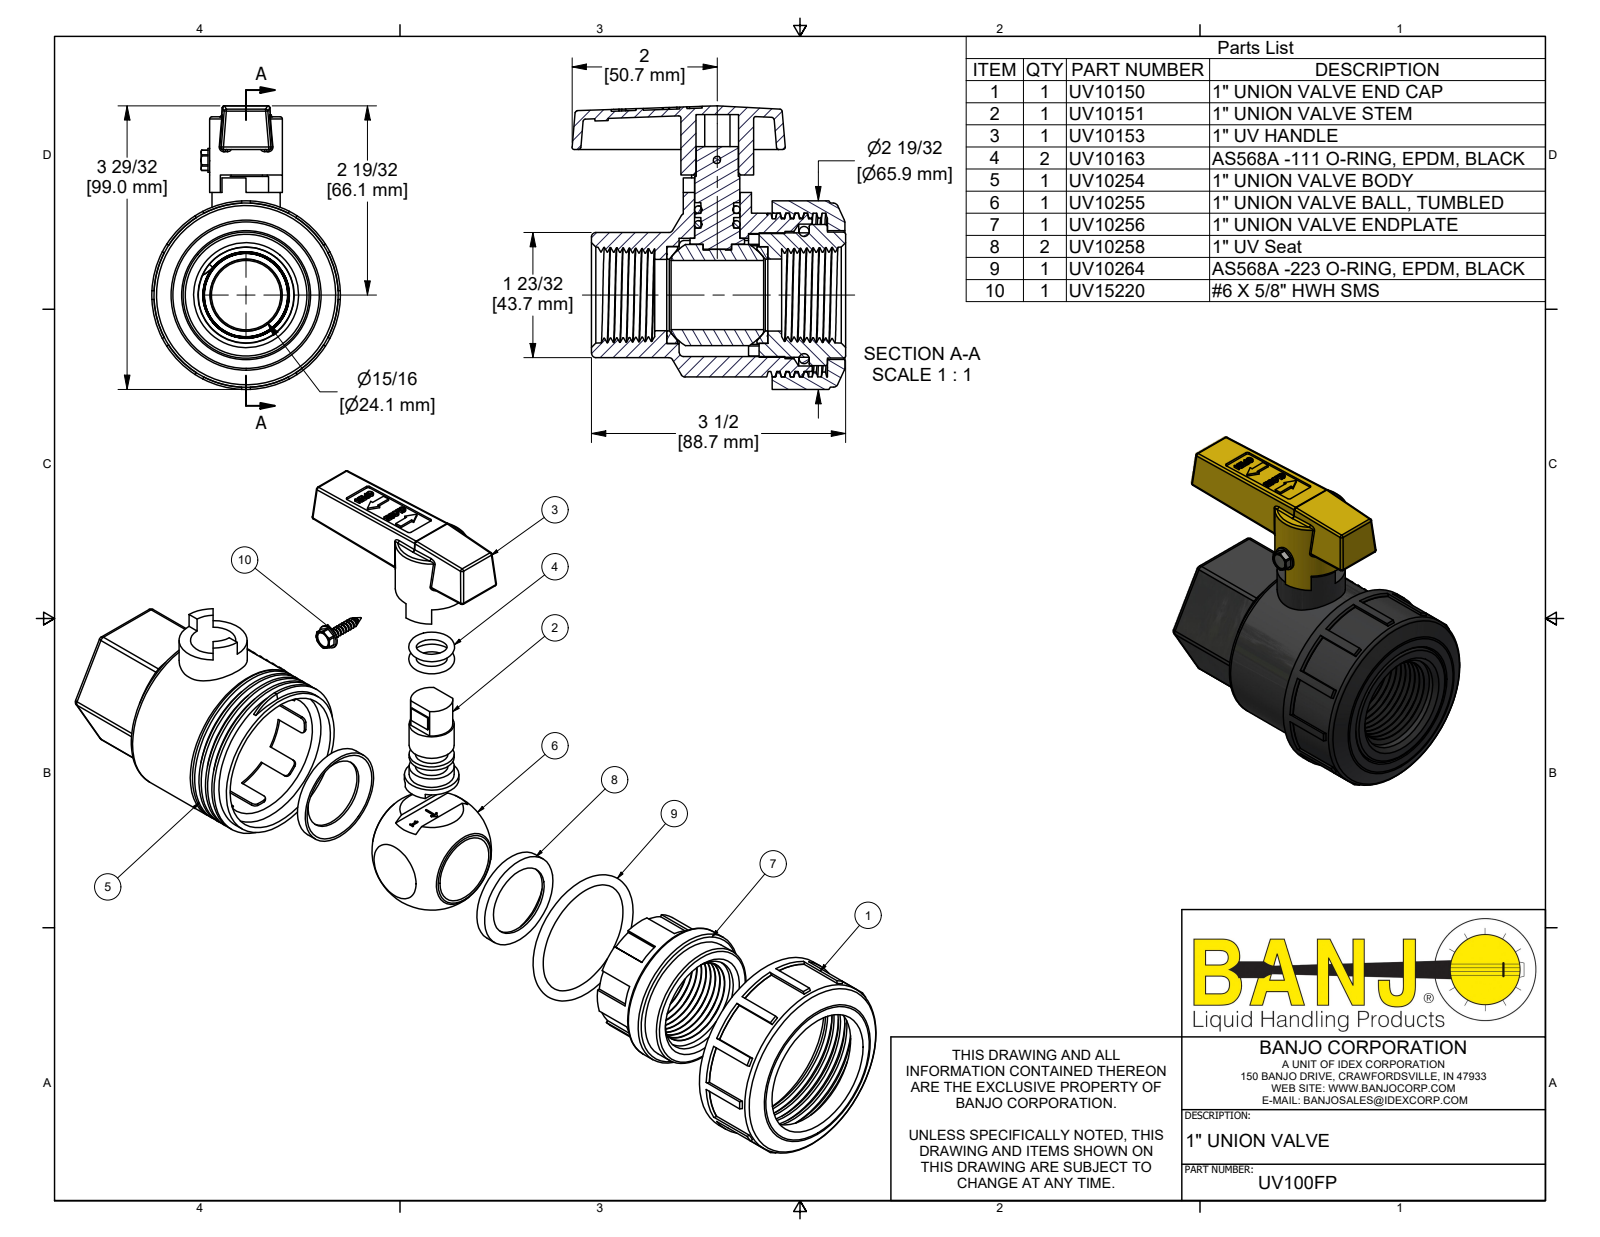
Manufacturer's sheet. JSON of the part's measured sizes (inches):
{"part_name": "UV100FP; UV10254; UV10163; UV10255 (+8 more)", "step_written_by": "Autodesk Inventor 2022 (AUTOMOTIVE_DESIGN)", "units": "inches", "bodies": {"solids": 12, "faces": 841, "planar": 357, "cylindrical": 174, "other": 310}, "overall_size": [3.899, 3.76, 2.594], "volume_in3": 10.15, "surface_area_in2": 124.4, "round_holes": [[0.585, 1], [0.625, 1], [0.95, 1], [0.98, 1], [0.985, 1], [0.99, 1], [1.325, 1], [1.335, 1], [1.69, 1], [1.75, 1], [1.77, 1], [1.95, 1]], "round_bosses_or_shafts": [[2.594, 1], [2.53, 1], [2.25, 1], [2.097, 1], [1.94, 1], [1.73, 1], [1.71, 1], [1.33, 1]], "partial_cylinders_radius": [[0.03, 40], [0.06, 24], [0.125, 3], [0.139, 1], [0.29, 1], [0.601, 1], [0.63, 1], [0.825, 1]], "face_to_face_distances": [1.72, 0.06, 0.165, 0.12, 0.76, 1.448, 2.208, 0.24, 1.388, 0.82]}
